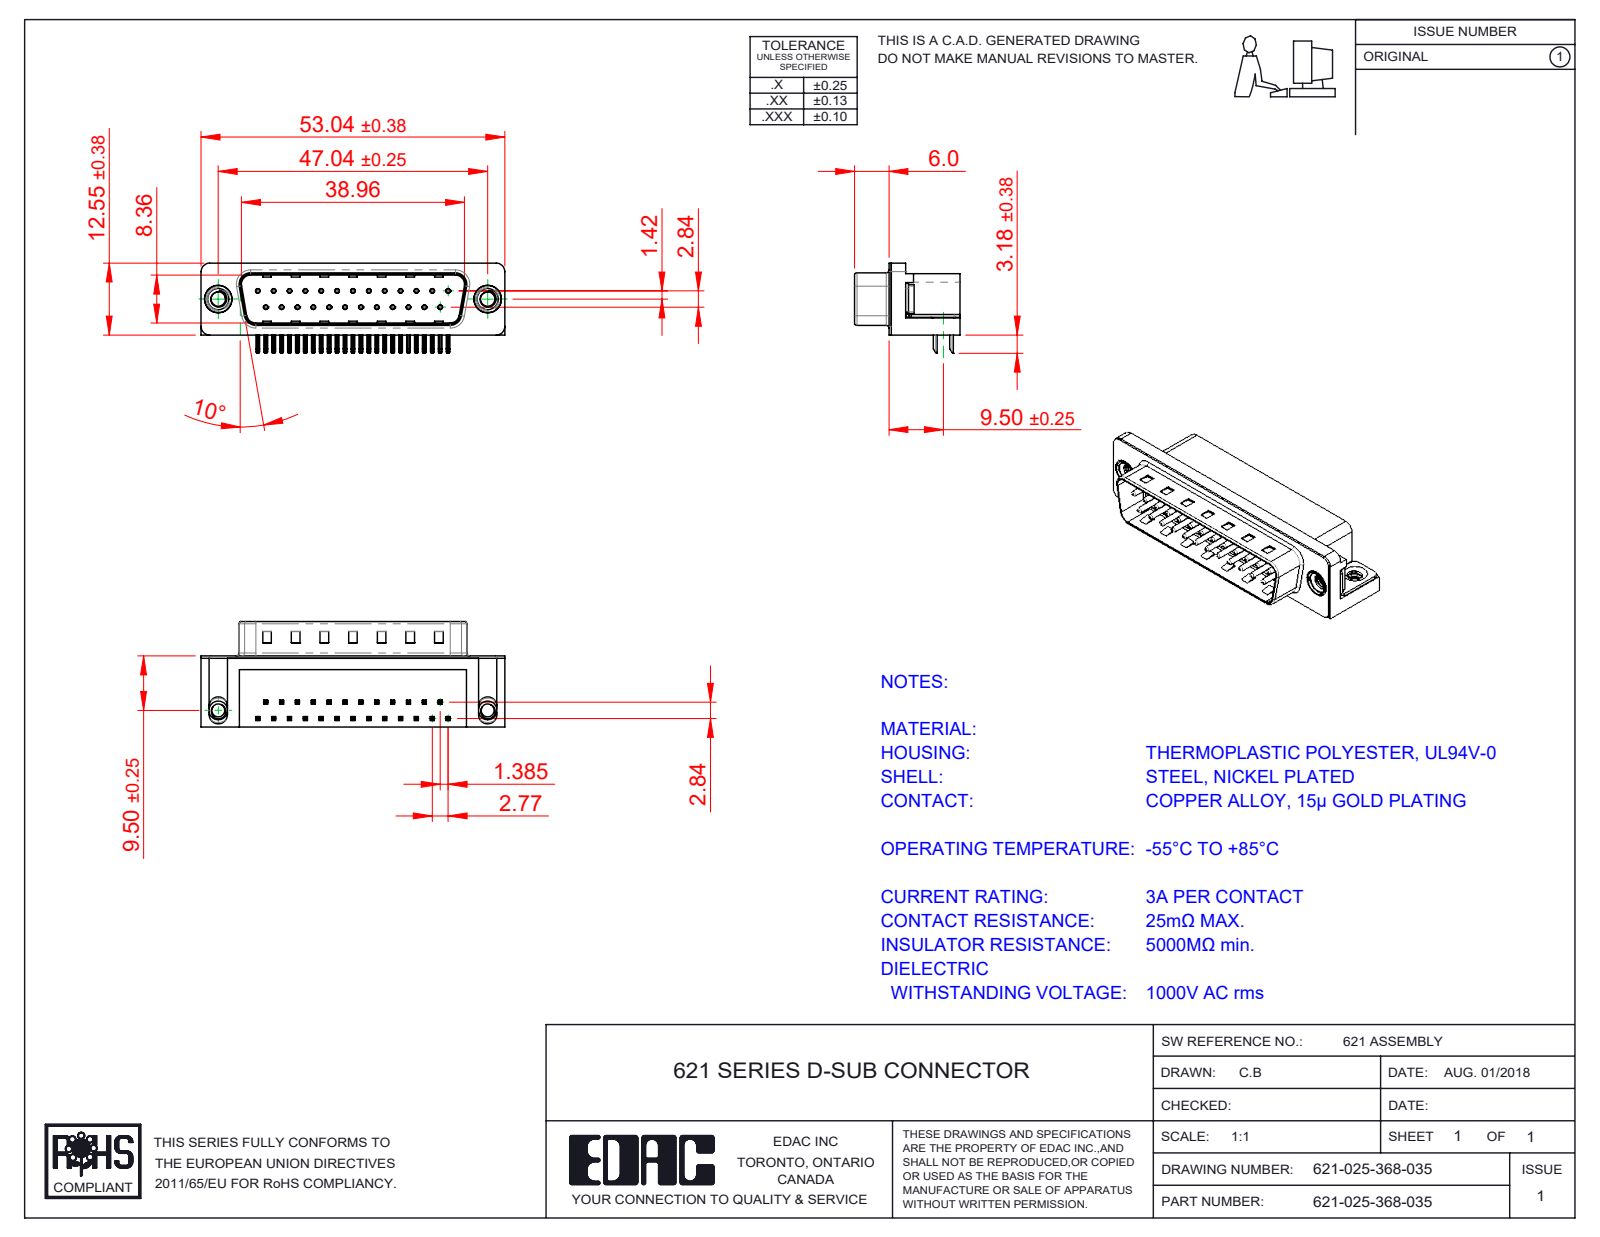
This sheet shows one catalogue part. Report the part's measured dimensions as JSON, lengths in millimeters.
{"part_name": "621 Housing_25 Socket; 621 Shell_25 Socket; 621 Contact Top; 621 Contact Bottom (+3 more)", "step_written_by": "SolidWorks 2016 (CONFIG_CONTROL_DESIGN)", "units": "millimeters", "bodies": {"solids": 31, "faces": 2303, "planar": 1437, "cylindrical": 671, "other": 195}, "overall_size": [53.04, 18.4, 16.25], "volume_mm3": 6342, "surface_area_mm2": 7692, "round_holes": [[0.35, 25], [0.8, 25], [2.5, 2], [4, 2], [4.8, 2], [5, 2]], "round_bosses_or_shafts": [[0.75, 25], [4.9, 2], [4.75, 2], [3.9, 2]], "partial_cylinders_radius": [[0.25, 108], [0.12, 50], [1, 16], [0.5, 14], [1.6, 8], [1.5, 7], [0.32, 4], [0.9, 4]], "face_to_face_distances": [0.4, 12, 10.35, 2.1, 8.76, 10.46, 10.86, 1.7, 12.4, 9], "hole_center_spacings": [3.16, 2.77, 5.54, 8.31, 11.08, 13.85, 16.62, 5.03]}
